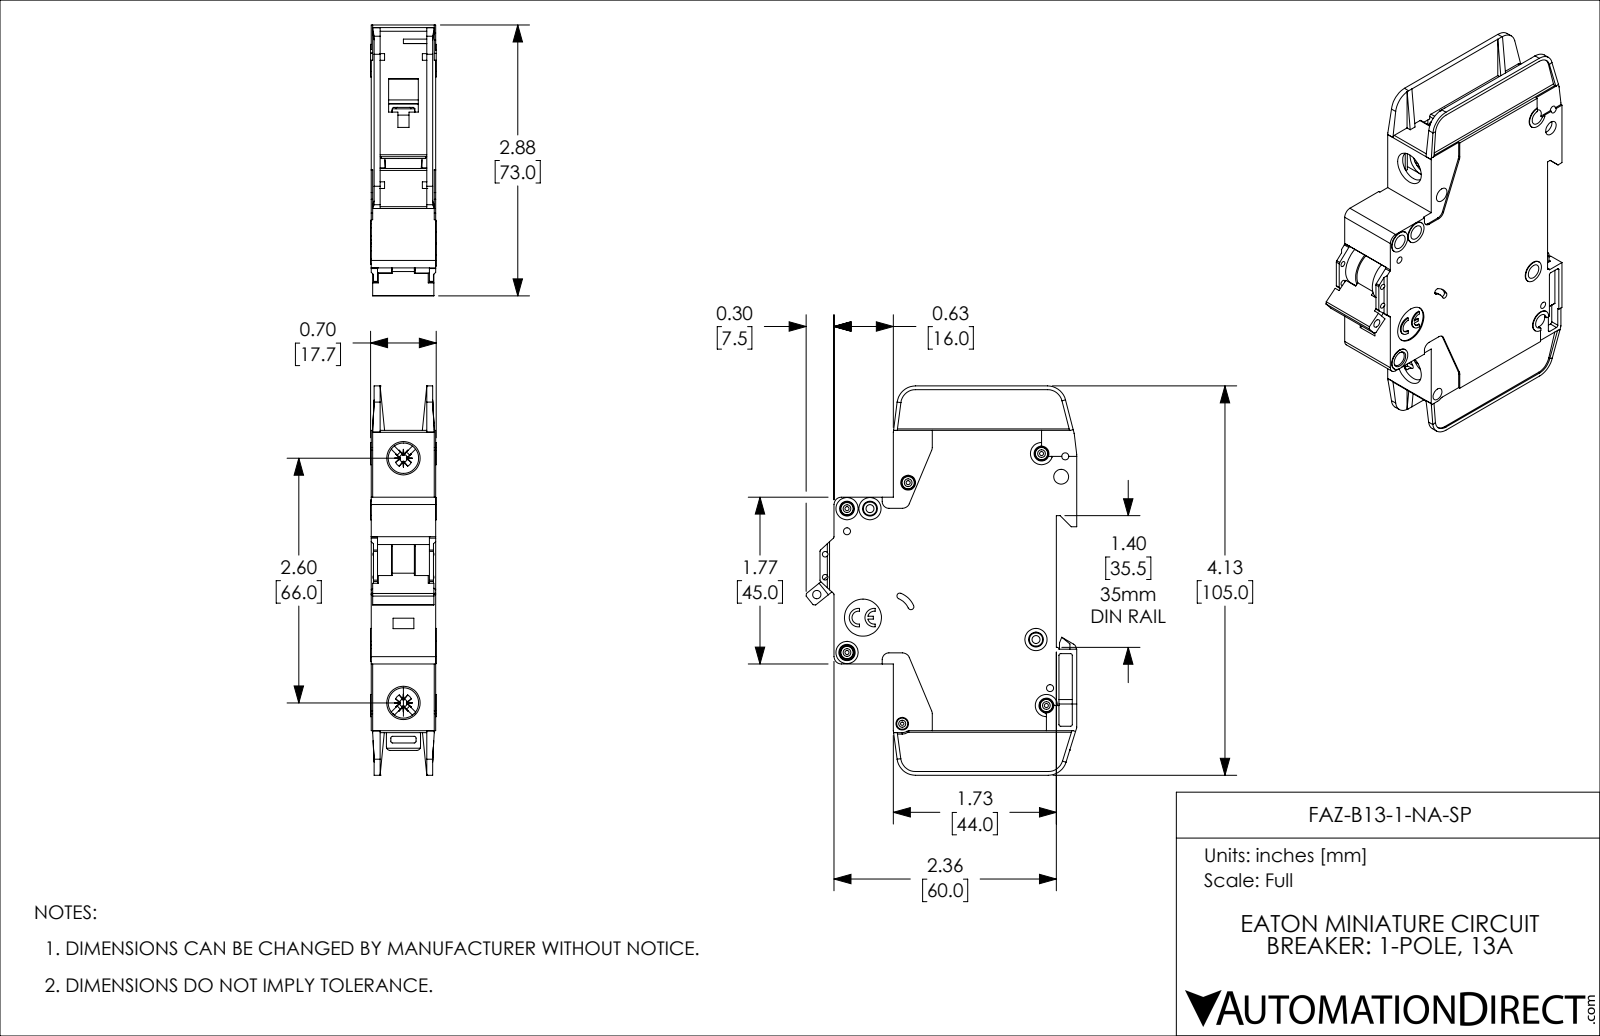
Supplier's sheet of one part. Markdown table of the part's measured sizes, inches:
| quantity | value |
| --- | --- |
| part name | FAZ-B13-1-NA-SP |
| STEP written by | SolidWorks 2019 (AUTOMOTIVE_DESIGN) |
| units | inches |
| bodies | 1 solid, 1127 faces (671 planar, 357 cylindrical, 99 other) |
| overall size | 4.134 × 2.876 × 0.697 |
| volume | 4.682 in³ |
| surface area | 41.01 in² |
| round holes (diameter × count) | 0.157 × 8, 0.043 × 5, 0.075 × 4, 0.059 × 2, 0.085 × 2, 0.323 × 2, 0.035 × 1, 0.089 × 1, 0.098 × 1, 0.134 × 1, 0.394 × 1 |
| round bosses / shafts (diameter × count) | 0.13 × 5, 0.236 × 4, 0.118 × 2, 0.098 × 1 |
| partial cylindrical surfaces (radius × count) | 0.02 × 42, 0.016 × 10, 0.039 × 10, 0.079 × 8, 0.197 × 5, 0.008 × 4, 0.026 × 4, 0.043 × 4 |
| main face-to-face distances | 0.047, 0.685, 0.591, 0.638, 0.094, 0.543, 0.016, 0.031, 0.496, 0.575 |
| hole center spacings | 0.244, 0.537, 0.87, 0.189, 0.199, 0.204, 0.221, 0.24 |
